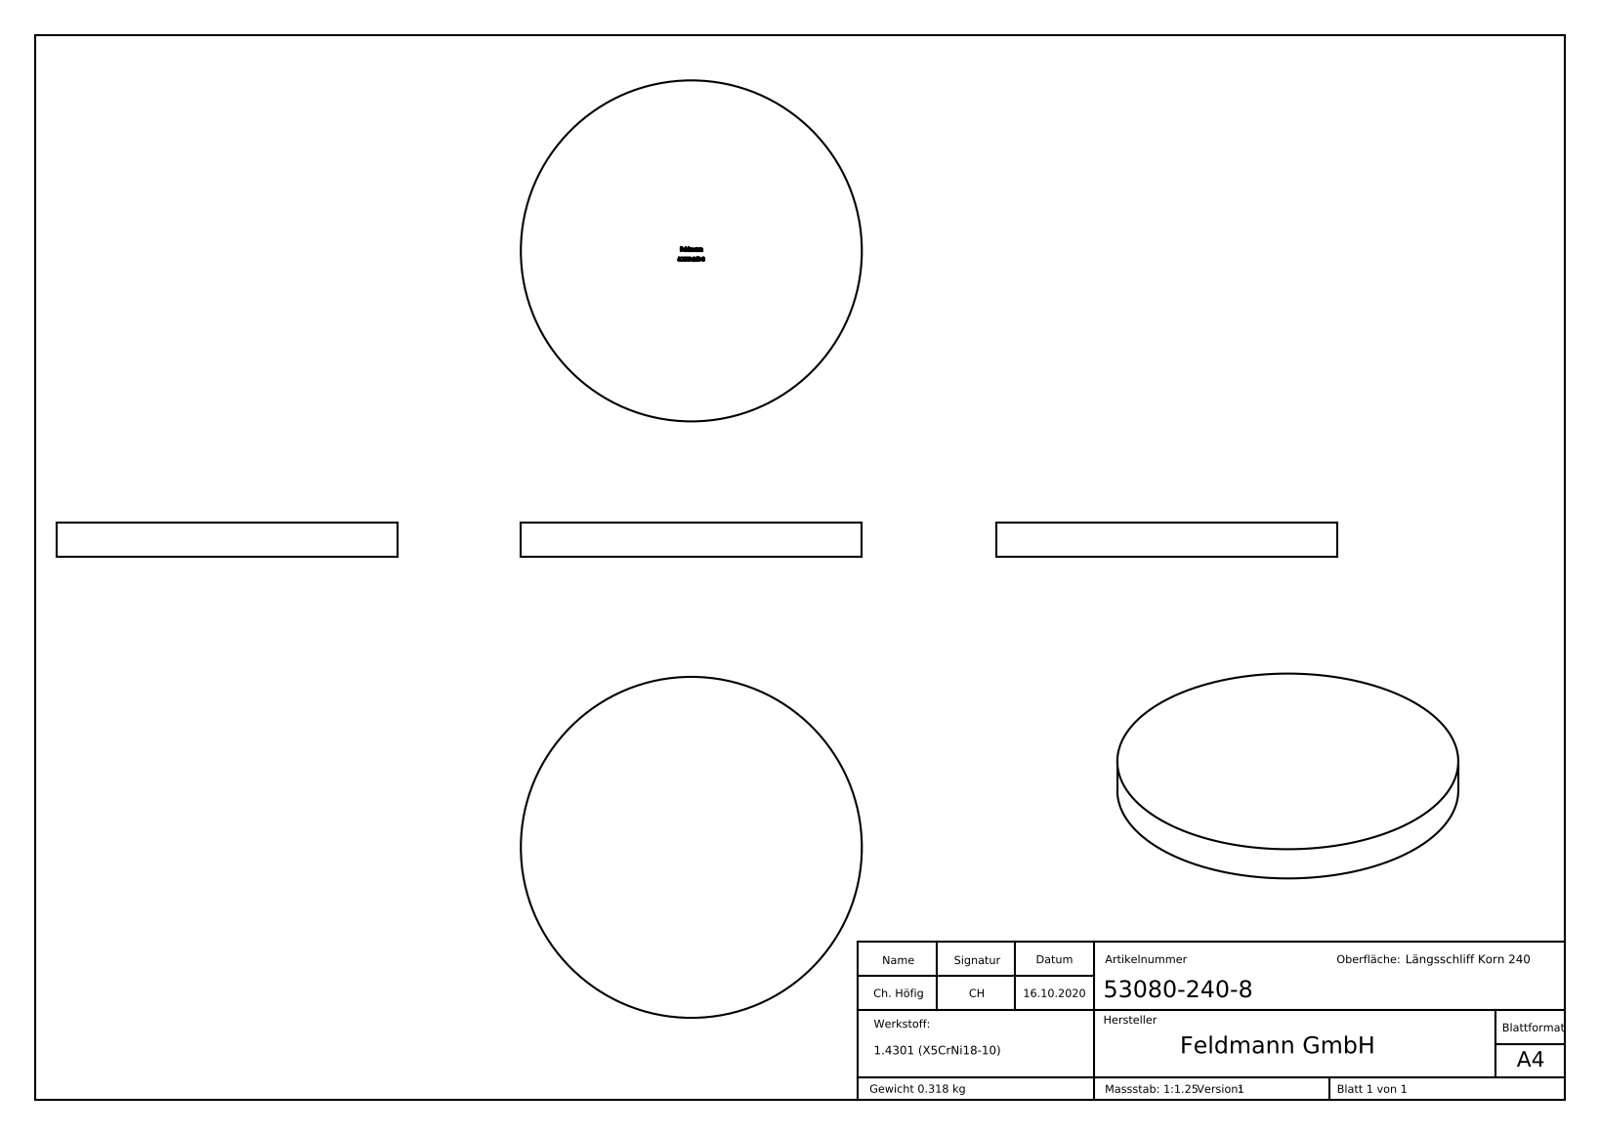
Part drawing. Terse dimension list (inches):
name: 53080-240-8
written by: SolidWorks 2018 (CONFIG_CONTROL_DESIGN)
unit: in
bodies: 1 solid, 261 faces (122 planar, 2 cylindrical, 137 other)
size: 3.15 × 3.15 × 0.315
volume: 2.454 in³; area: 18.71 in²
bosses: 1× ⌀3.15
face distances: 0.315, 0.311, 0.033, 0.07, 0.103, 0.03, 0.096, 0.109, 0.106, 0.039
